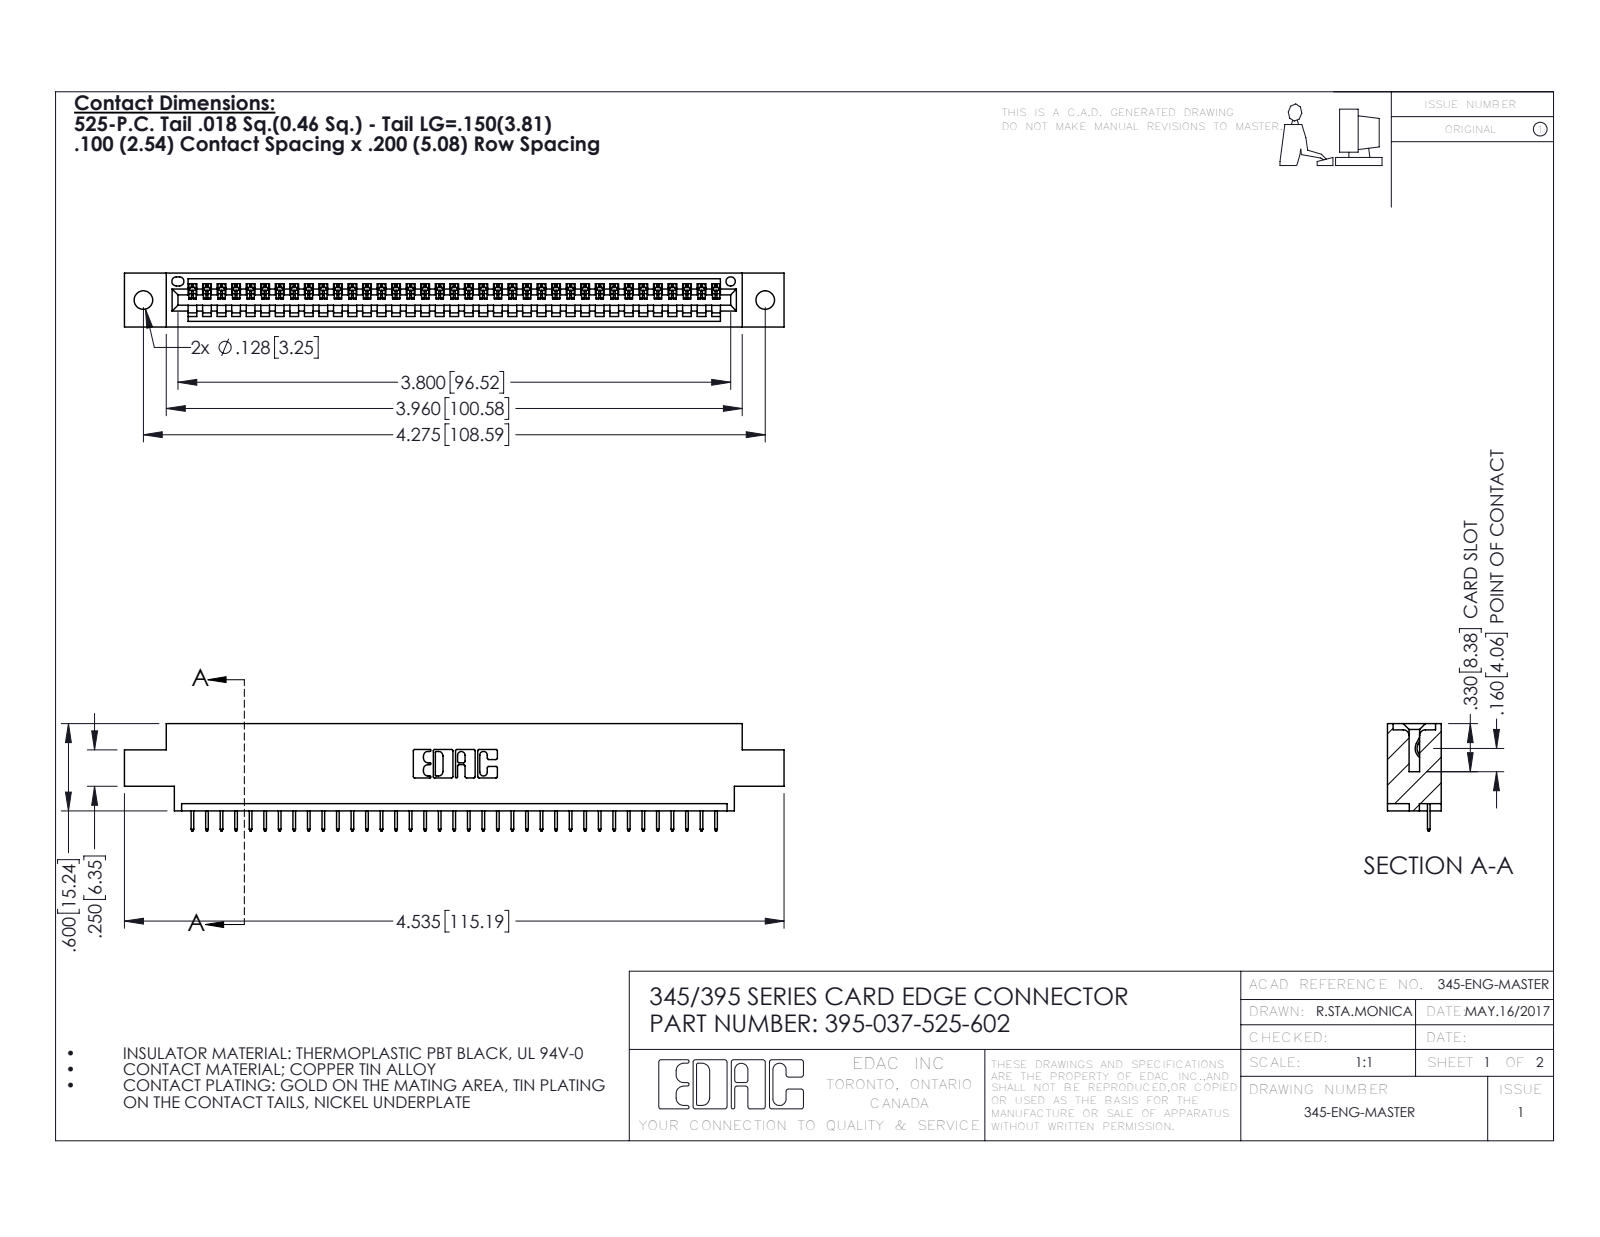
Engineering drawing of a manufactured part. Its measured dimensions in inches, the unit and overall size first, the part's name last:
Units: inches
Overall size (bounding box): 4.535 × 0.737 × 0.37
Round holes (diameter × count): ⌀0.128 ×2, ⌀0.064 ×1
Partial cylindrical surfaces — rounded edges, fillets, slot ends (radius × count): R0.006 ×74, R0.01 ×22, R0.007 ×6, R0.031 ×6, R0.026 ×3, R0.031 ×2, R0.04 ×2, R0.014 ×1
Main face-to-face distances: 0.072, 0.298, 0.37, 0.2, 0.098, 0.272, 0.025, 0.225, 0.175, 0.072
Hole centre spacings: 0.27, 4.039, 4.275
Volume: 0.647 in³ · Surface area: 20.72 in²
Bodies: 38 solids, 2424 faces (1786 planar, 638 cylindrical, 0 other)
Part name (STEP PRODUCT): 395-037-525-602; 345 Part_0.170 Offset - 0.128 Dia; 345-292-001_345-293-125
STEP written by: SolidWorks 2020 (CONFIG_CONTROL_DESIGN)
